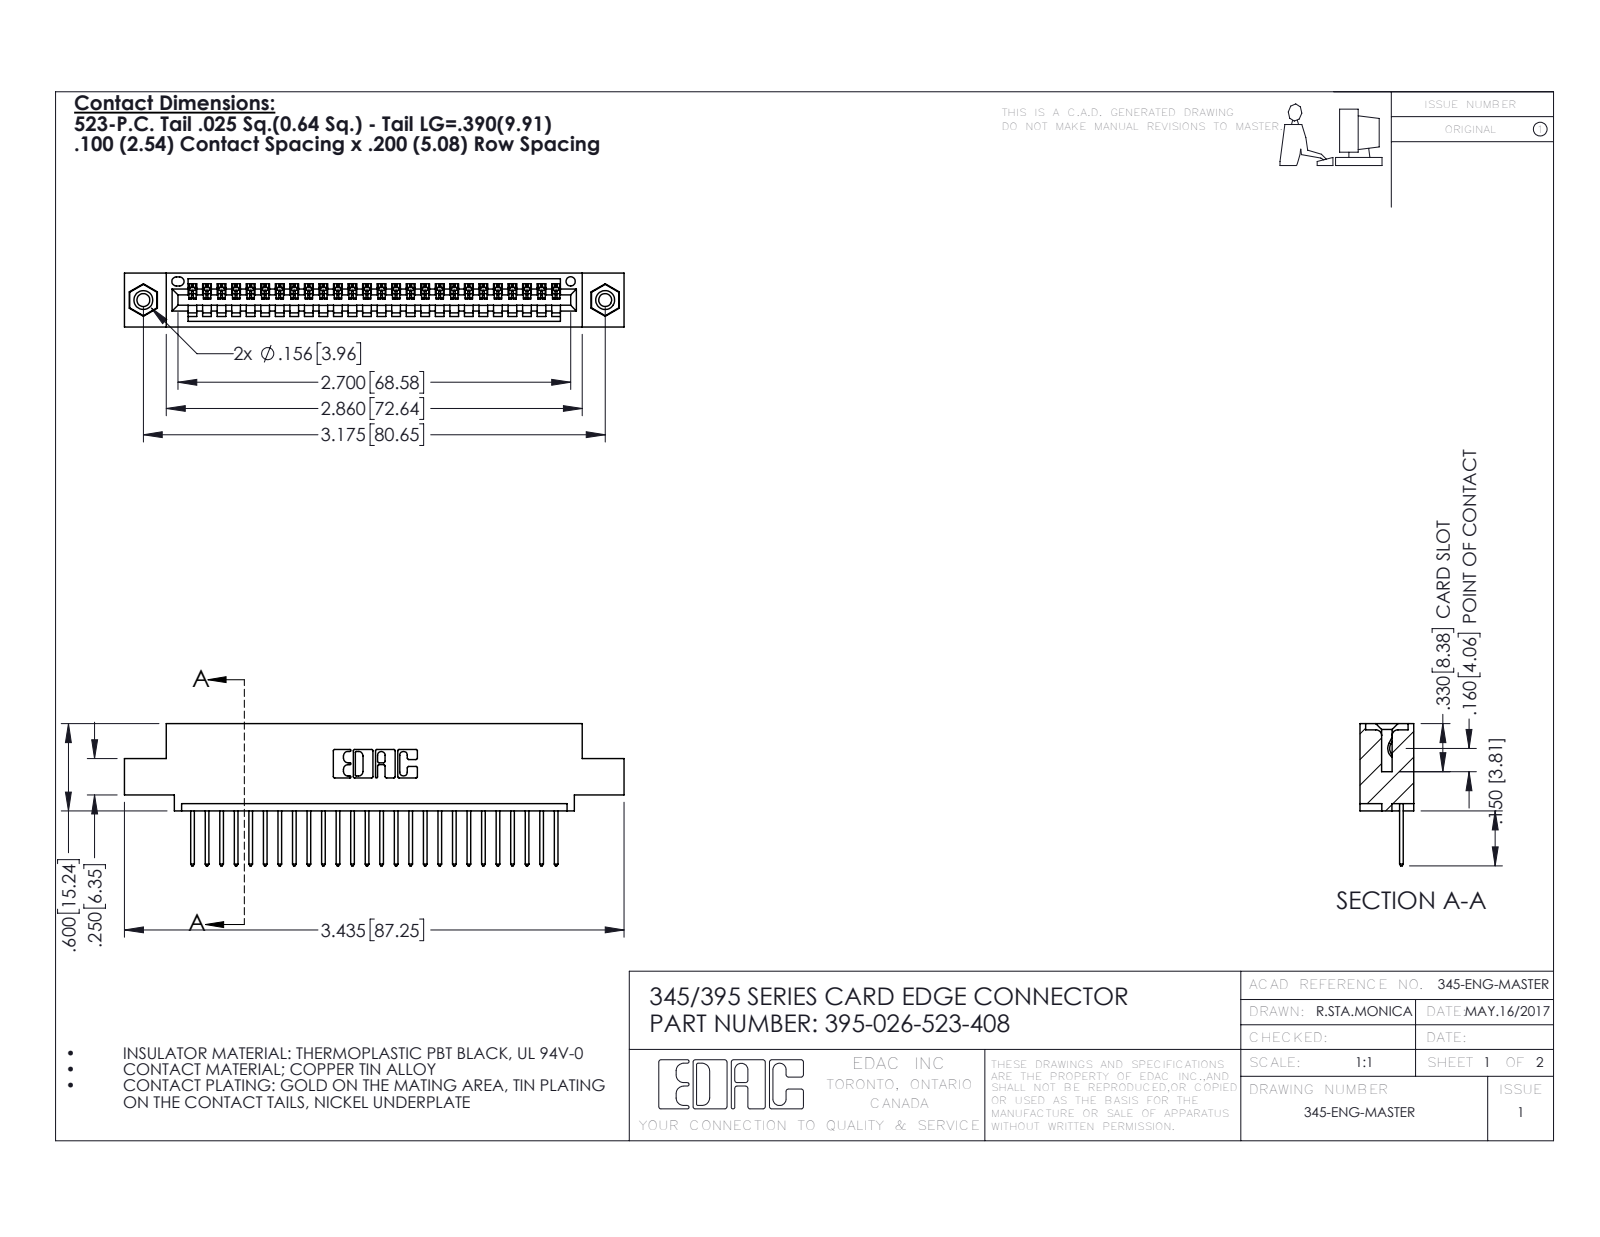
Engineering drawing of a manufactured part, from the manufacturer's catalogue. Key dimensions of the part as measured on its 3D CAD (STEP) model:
Part name (STEP PRODUCT): 395-026-523-408; 345-292-001_345-293-123; 345-250-001_345-250-003-102; 345 Part_0.110 Offset - 0.156 Dia-TI
STEP written by: SolidWorks 2016 (CONFIG_CONTROL_DESIGN)
Units: inches
Bodies: 29 solids, 1698 faces (1156 planar, 526 cylindrical, 16 other)
Overall size (bounding box): 3.435 × 0.977 × 0.37
Volume: 0.492 in³ · Surface area: 16.48 in²
Round holes (diameter × count): ⌀0.089 ×2, ⌀0.125 ×2, ⌀0.156 ×2, ⌀0.064 ×1
Round bosses / shafts (diameter × count): ⌀0.155 ×2
Partial cylindrical surfaces — rounded edges, fillets, slot ends (radius × count): R0.006 ×52, R0.01 ×52, R0.01 ×22, R0.007 ×6, R0.031 ×6, R0.026 ×3, R0.031 ×2, R0.04 ×2
Main face-to-face distances: 0.072, 0.298, 0.2, 0.37, 0.098, 0.272, 0.025, 0.225, 0.149, 0.072
Hole centre spacings: 0.27, 2.94, 3.175
